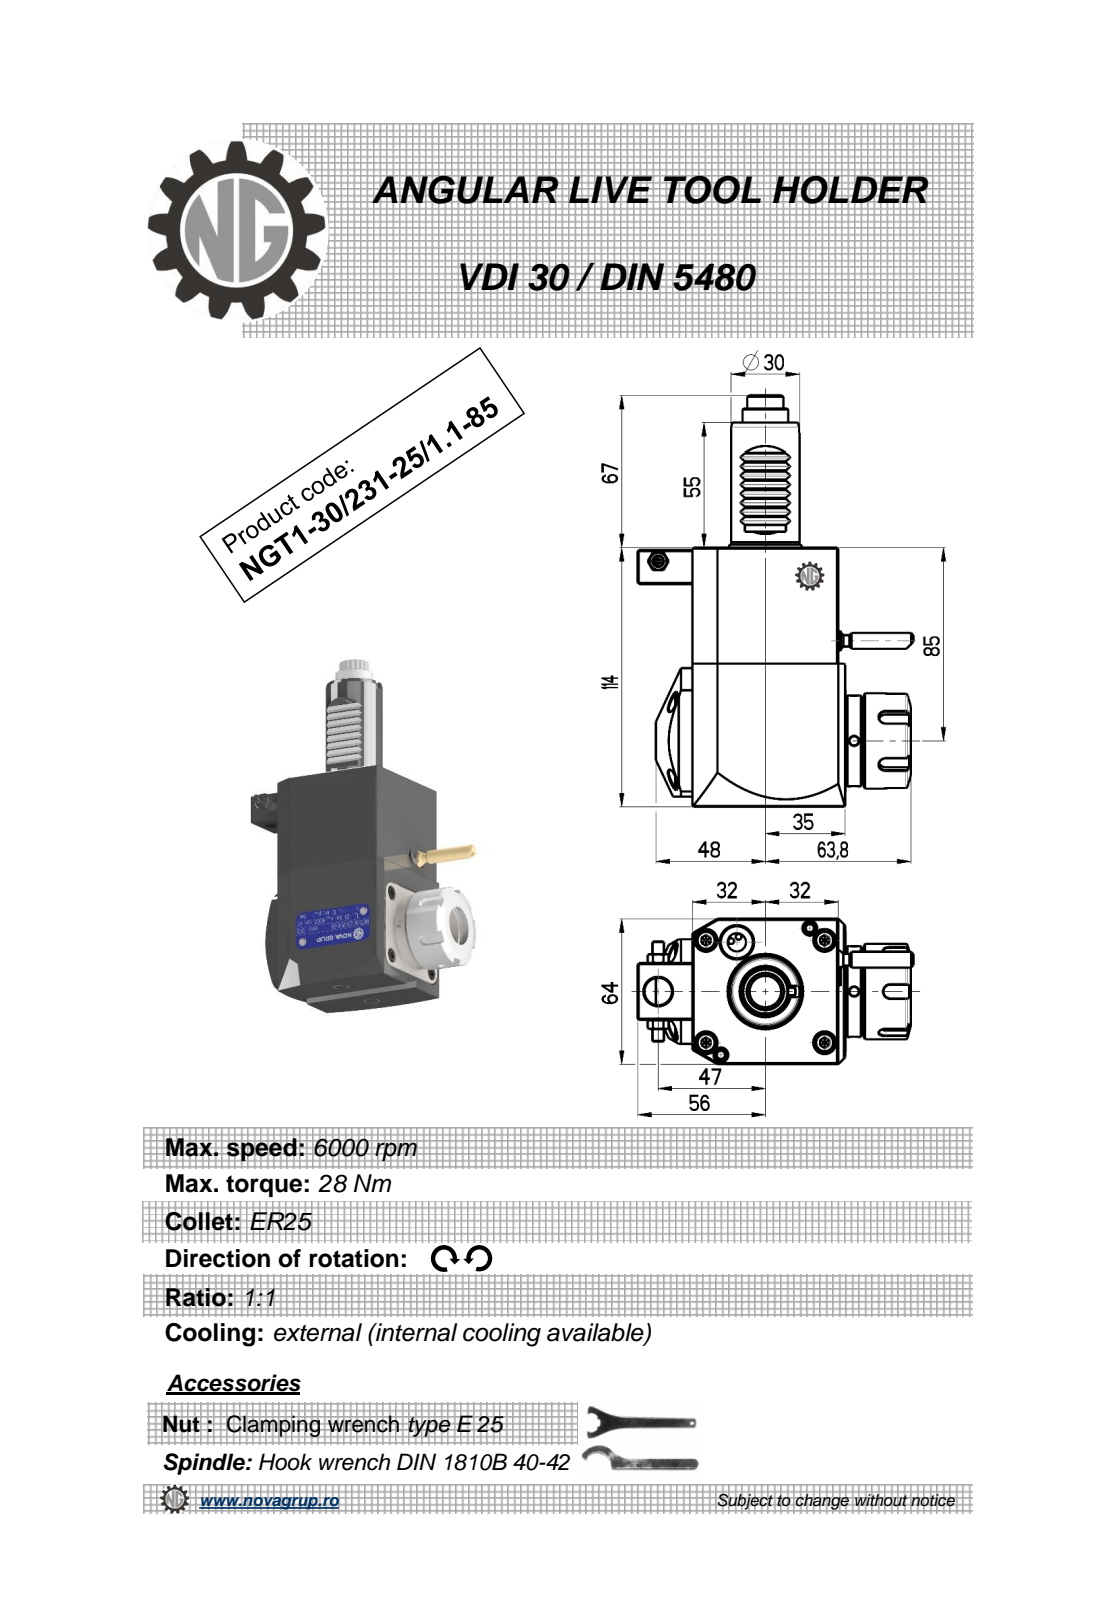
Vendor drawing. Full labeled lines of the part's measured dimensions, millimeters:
Part name (STEP PRODUCT): NGT1_30_231_25_1_1_85
STEP written by: PRO/ENGINEER BY PARAMETRIC TECHNOLOGY CORPORATION, 2010280 (CONFIG_CONTROL_DESIGN)
Units: millimetres
Bodies: 1 solid, 510 faces (188 planar, 161 cylindrical, 161 other)
Overall size (bounding box): 181 × 120.88 × 65.6
Volume: 576 150 mm³ · Surface area: 54 673 mm²
Round holes (diameter × count): ⌀4 ×2, ⌀2.5 ×1, ⌀3 ×1, ⌀4.2 ×1, ⌀9.5 ×1, ⌀12 ×1, ⌀20.3 ×1
Round bosses / shafts (diameter × count): ⌀8.96 ×2, ⌀5 ×2, ⌀42 ×1, ⌀40 ×1, ⌀33 ×1, ⌀30 ×1, ⌀20 ×1, ⌀7 ×1
Partial cylindrical surfaces — rounded edges, fillets, slot ends (radius × count): R1.98 ×36, R0.26 ×12, R0.3 ×8, R3 ×5, R3.5 ×4, R160 ×2, R7.08 ×1, R7.92 ×1
Main face-to-face distances: 64, 114, 67.2, 3.2, 67, 3, 0.5, 55, 16, 4
Hole centre spacings: 35.39, 46.17, 76.5, 85.95, 116.74
